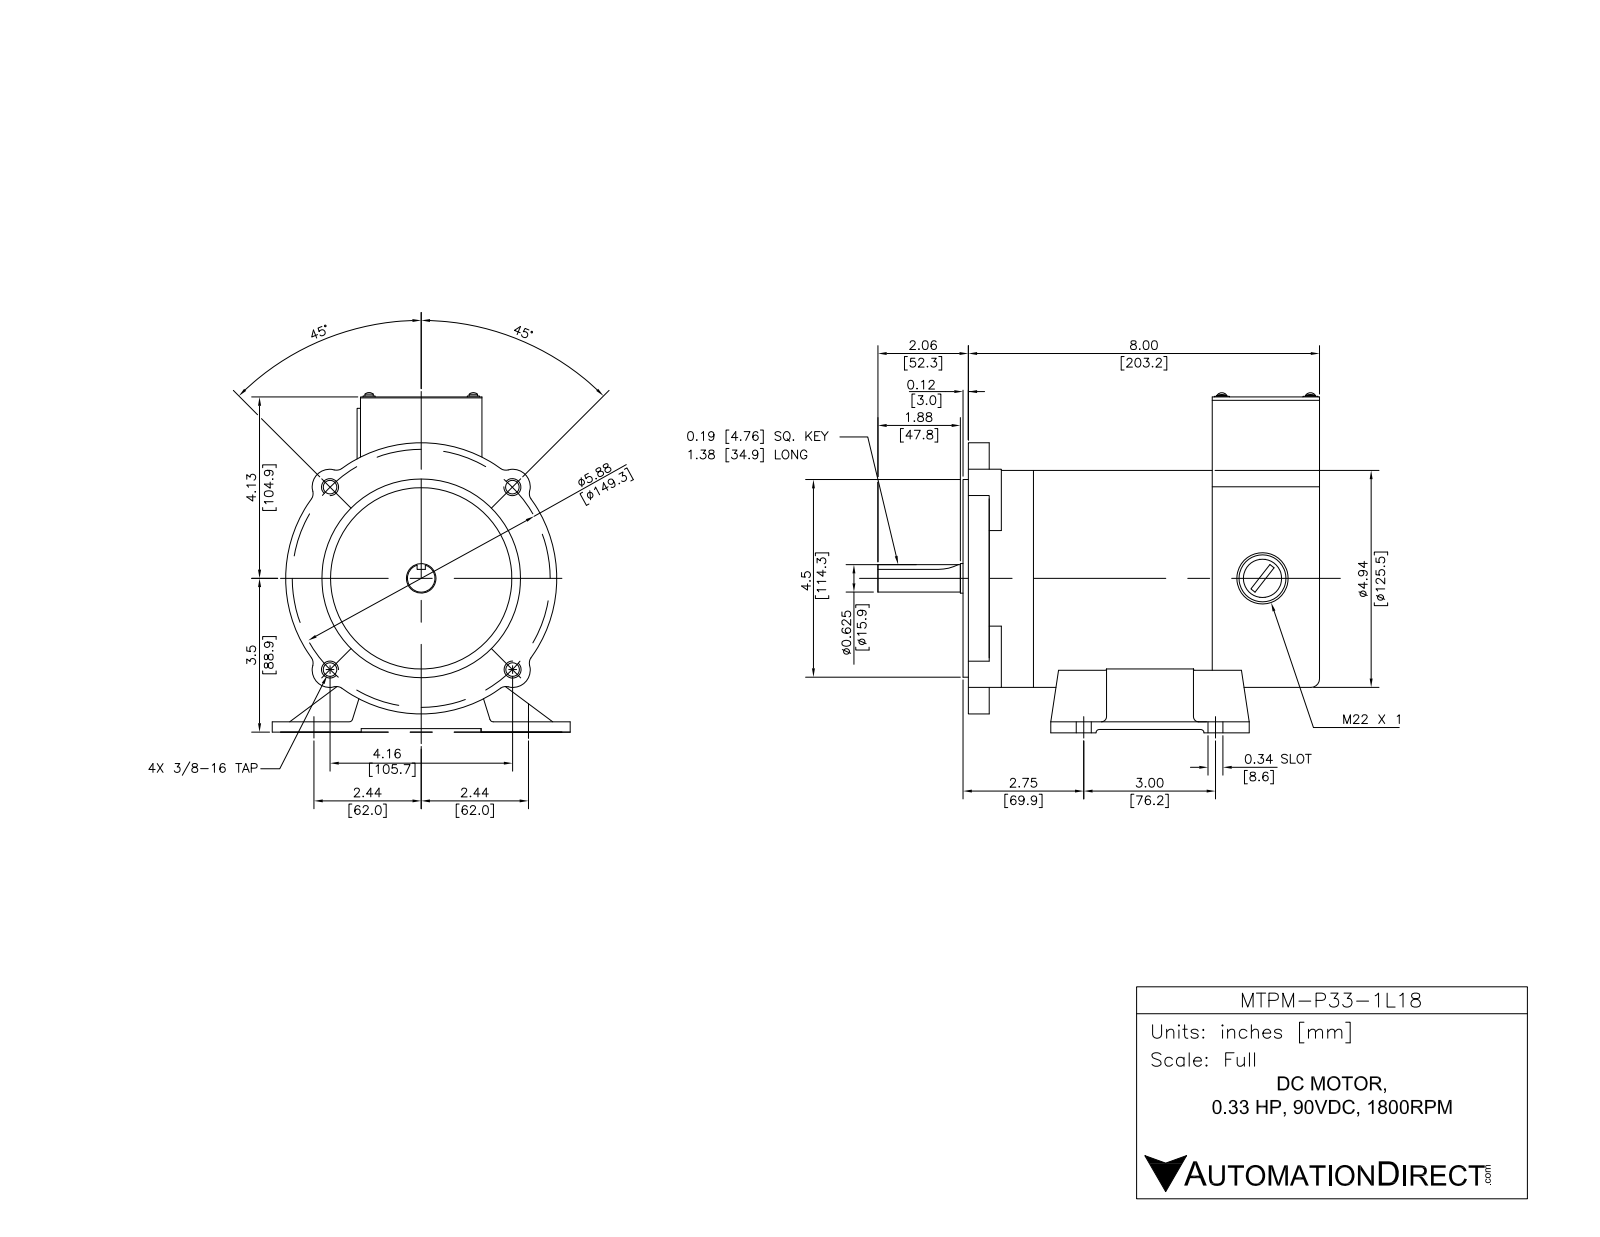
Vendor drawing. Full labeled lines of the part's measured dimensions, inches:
Part name (STEP PRODUCT): WPMDC13-18-90V-56CB wkey cut
STEP written by: SolidWorks 2017 (AUTOMOTIVE_DESIGN)
Units: inches
Bodies: 28 solids, 1248 faces (366 planar, 571 cylindrical, 311 other)
Overall size (bounding box): 10.106 × 7.521 × 6.496
Volume: 57.44 in³ · Surface area: 604.1 in²
Round holes (diameter × count): ⌀0.197 ×8, ⌀0.13 ×6, ⌀0.098 ×2, ⌀0.169 ×2, ⌀0.205 ×2, ⌀0.236 ×2, ⌀0.276 ×2, ⌀0.299 ×2, ⌀0.374 ×2, ⌀0.394 ×2, ⌀0.728 ×2, ⌀1.575 ×2
Round bosses / shafts (diameter × count): ⌀0.157 ×6, ⌀0.354 ×4, ⌀0.331 ×4, ⌀1.929 ×2, ⌀0.39 ×2, ⌀6.142 ×1, ⌀4.937 ×1, ⌀4.74 ×1
Partial cylindrical surfaces — rounded edges, fillets, slot ends (radius × count): R0.197 ×38, R0.02 ×34, R0.039 ×28, R0.098 ×14, R0.236 ×10, R0.118 ×8, R0.157 ×8, R0.169 ×8
Main face-to-face distances: 0.098, 0.157, 0.079, 0.059, 8.028, 8.087, 7.929, 0.256, 0.276, 0.472
Hole centre spacings: 0.05, 1.187, 1.89, 2.166, 2.262, 2.362, 2.749, 0.104
